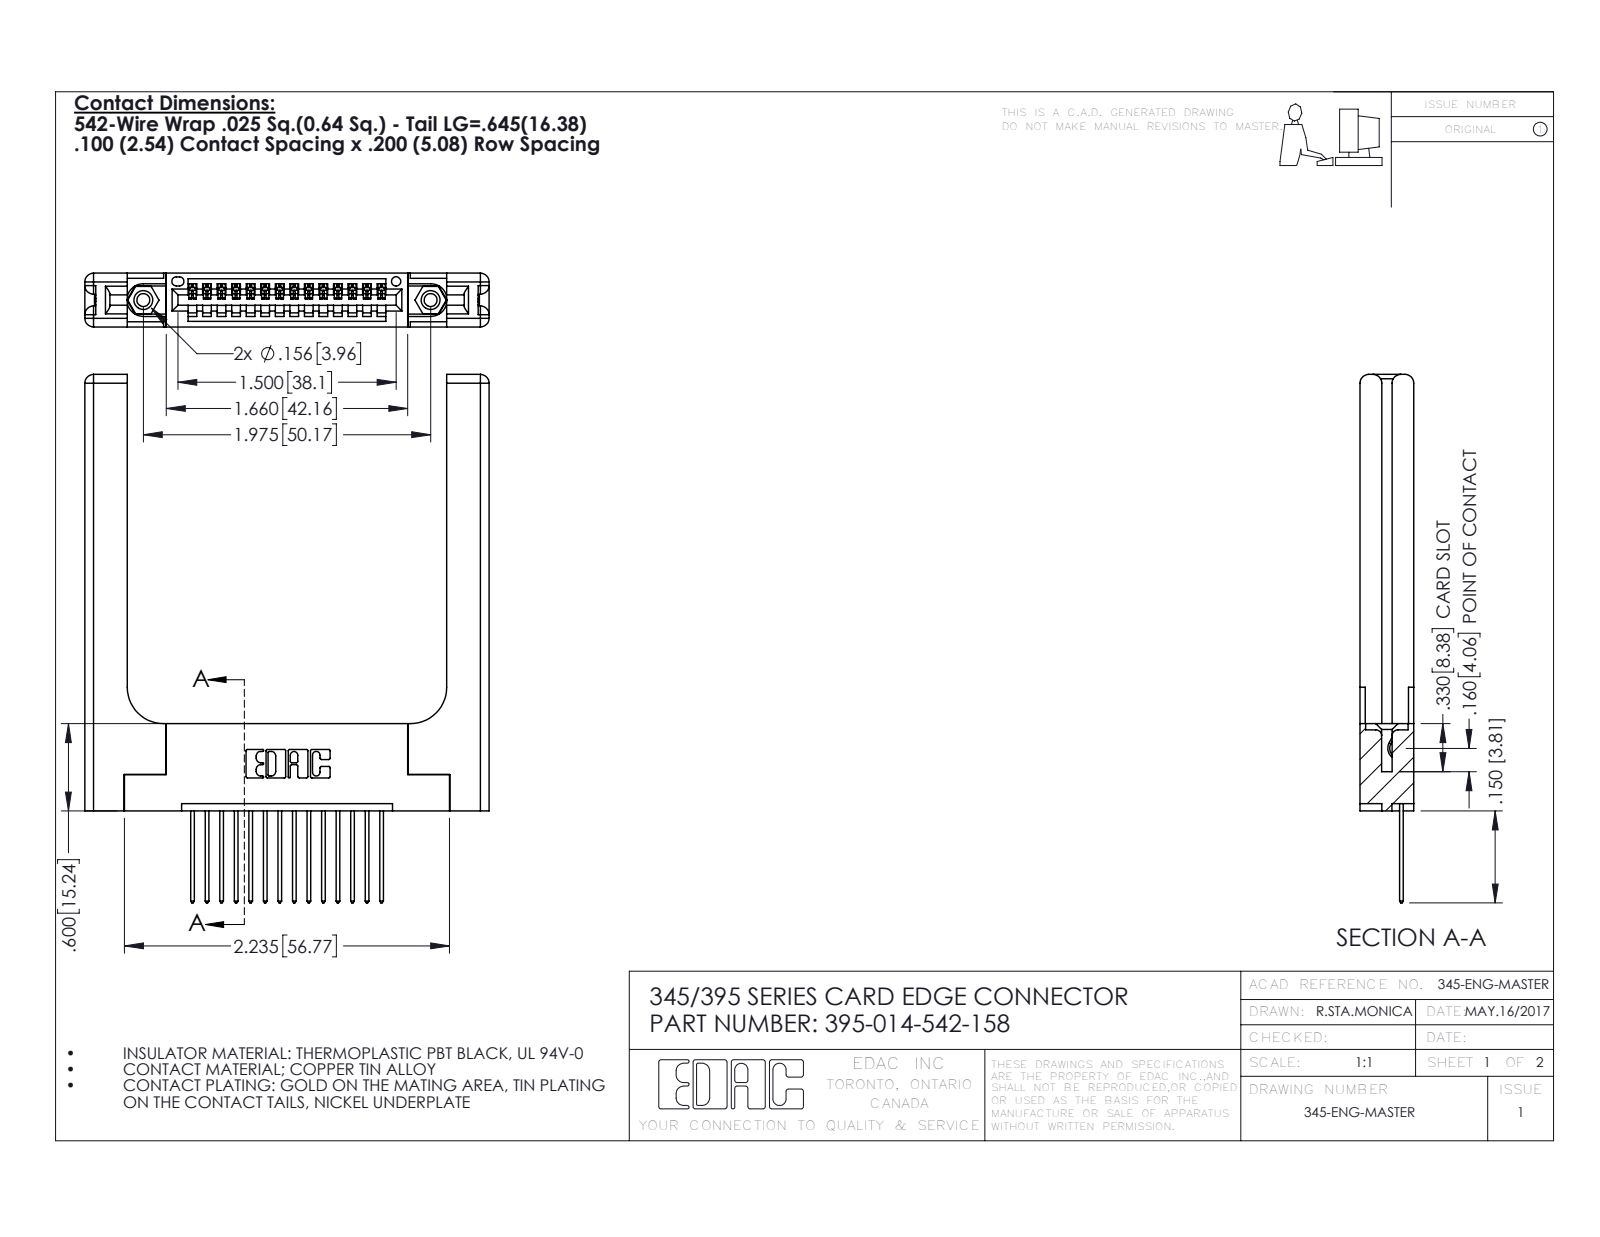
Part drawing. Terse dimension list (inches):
name: 345-250-001_345-250-001-102; 345 Part_Flush Mounting Lugs - 0.156 Dia-TH; 395-014-542-158; 345-292-001_345-293-142 (+1 more)
written by: SolidWorks 2016 (CONFIG_CONTROL_DESIGN)
unit: in
bodies: 19 solids, 1194 faces (788 planar, 346 cylindrical, 60 other)
size: 3.632 × 2.779 × 0.37
volume: 0.916 in³; area: 21.34 in²
holes: 2× ⌀0.089, 2× ⌀0.125, 2× ⌀0.156, 1× ⌀0.064
bosses: 2× ⌀0.155
rounds: 28× R0.006, 28× R0.01, 22× R0.01, 16× R0.06, 6× R0.007, 6× R0.031, 3× R0.026, 2× R0.03
face distances: 0.37, 0.072, 0.298, 0.15, 0.077, 0.2, 0.148, 0.22, 0.098, 0.272
hole spacings: 0.27, 1.742, 1.975
